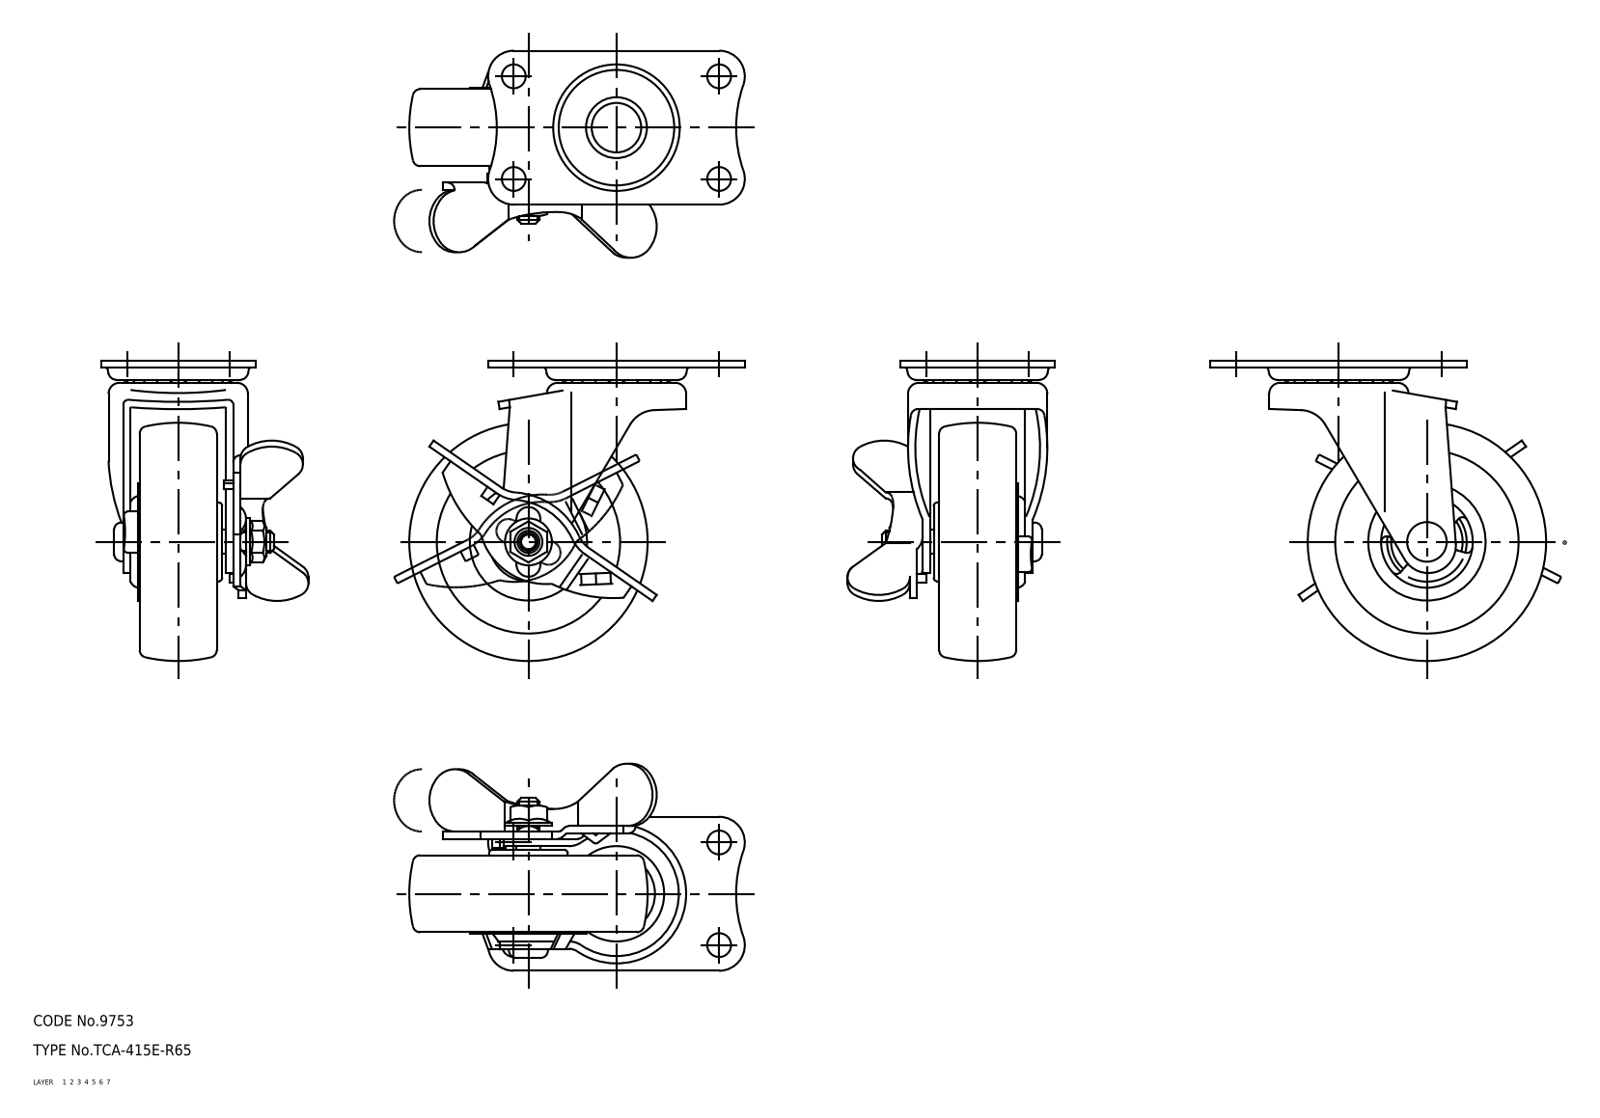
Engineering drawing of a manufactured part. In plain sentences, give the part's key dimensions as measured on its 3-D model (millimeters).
The part is named "lever; wheel; mounting plate; main shaft (+2 more)". Its 3-D file was written by "CADfix (AUTOMOTIVE_DESIGN)". It is 6 solids with 369 faces: 0 planar, 0 cylindrical and 369 other. Overall it measures 91.5 by 82 by 56.49 millimeters. Its volume is 90 580 cubic millimeters and its surface area 34 193 square millimeters.
